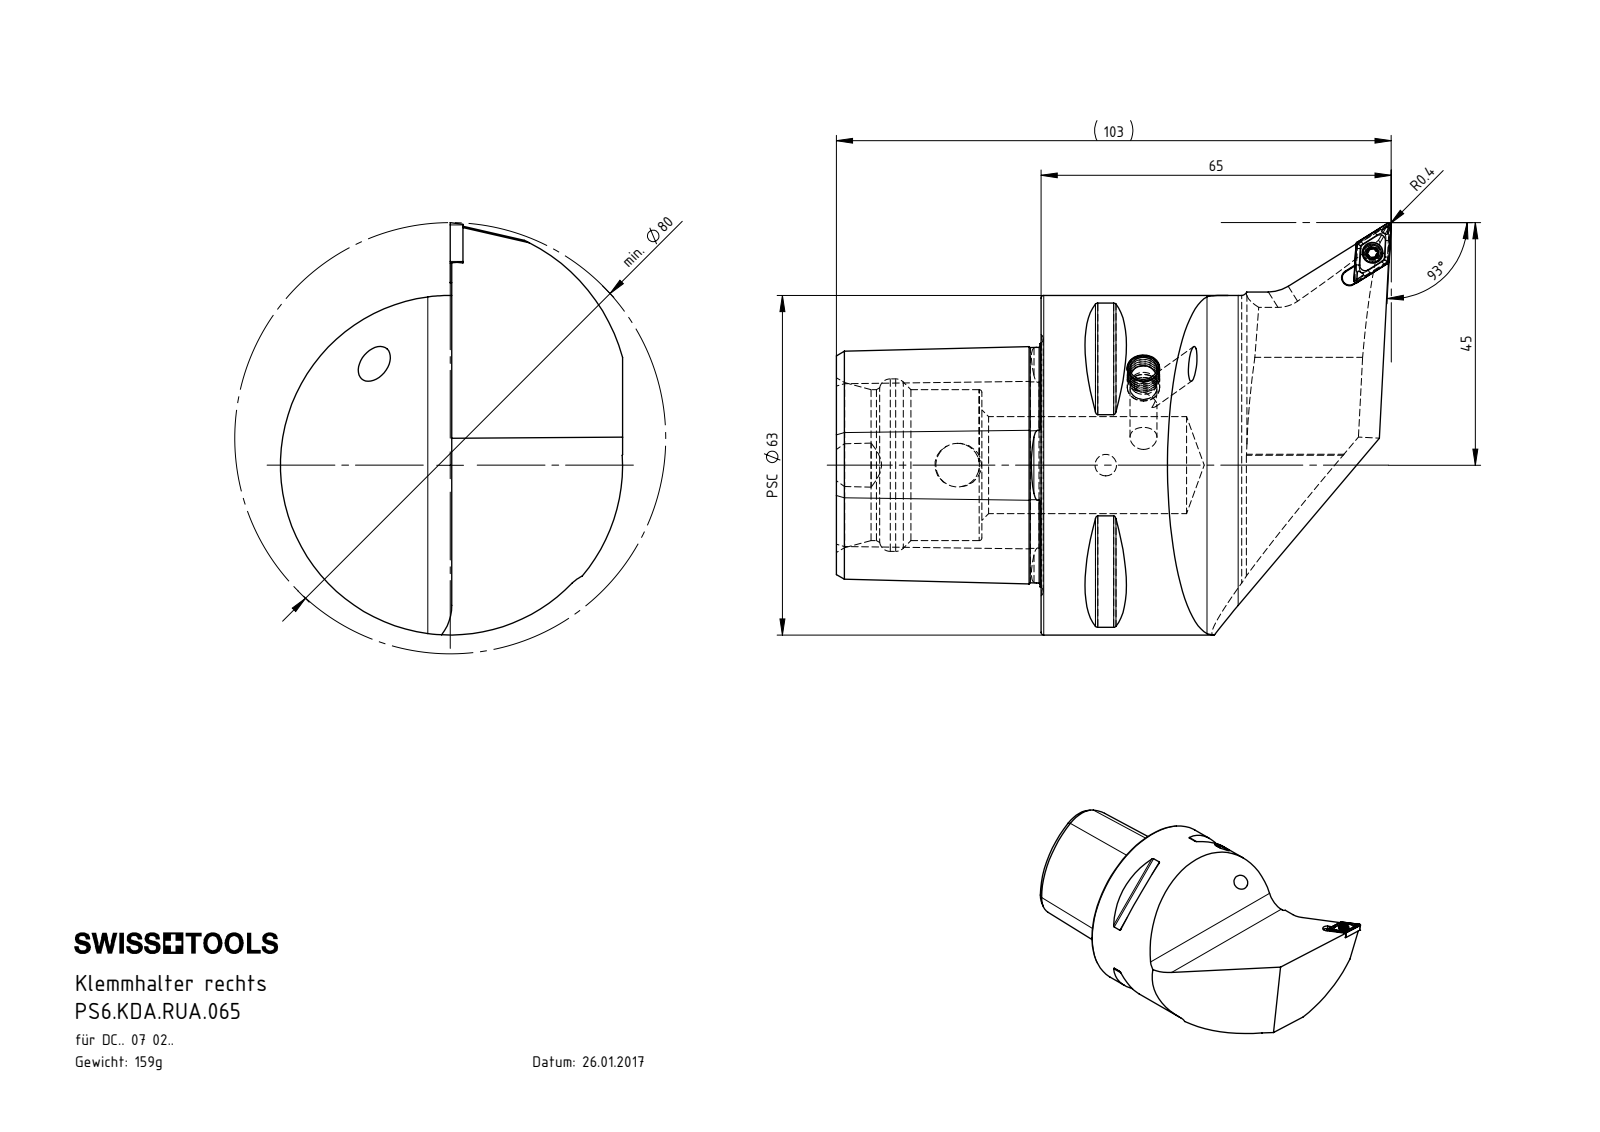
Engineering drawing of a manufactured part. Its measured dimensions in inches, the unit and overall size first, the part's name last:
Units: inches
Overall size (bounding box): 4.055 × 3.011 × 2.5
Round holes (diameter × count): ⌀0.197 ×3, ⌀0.081 ×1, ⌀0.11 ×1, ⌀0.152 ×1, ⌀0.157 ×1, ⌀0.236 ×1, ⌀0.319 ×1, ⌀0.709 ×1, ⌀1.102 ×1, ⌀1.26 ×1
Round bosses / shafts (diameter × count): ⌀2.48 ×1, ⌀0.236 ×1, ⌀0.134 ×1, ⌀0.098 ×1
Partial cylindrical surfaces — rounded edges, fillets, slot ends (radius × count): R0.02 ×8, R0.008 ×6, R0.014 ×5, R0.053 ×2, R0.236 ×2, R0.014 ×1, R0.276 ×1, R1.26 ×1
Main face-to-face distances: 1.496, 1.248, 0.98, 1.063, 0.433, 2.197, 1.488, 0.425, 1.166, 0.082
Hole centre spacings: 1.083, 2.489, 2.492, 3.404, 3.407
Volume: 9.618 in³ · Surface area: 42.75 in²
Bodies: 5 solids, 200 faces (57 planar, 46 cylindrical, 97 other)
Part name (STEP PRODUCT): PS6.KDA.RUA.065; DCMT070204; KVT_MB_600_060; PS6-KDA.RUA.065_A (+1 more)
STEP written by: SolidWorks 2017 (AUTOMOTIVE_DESIGN)
